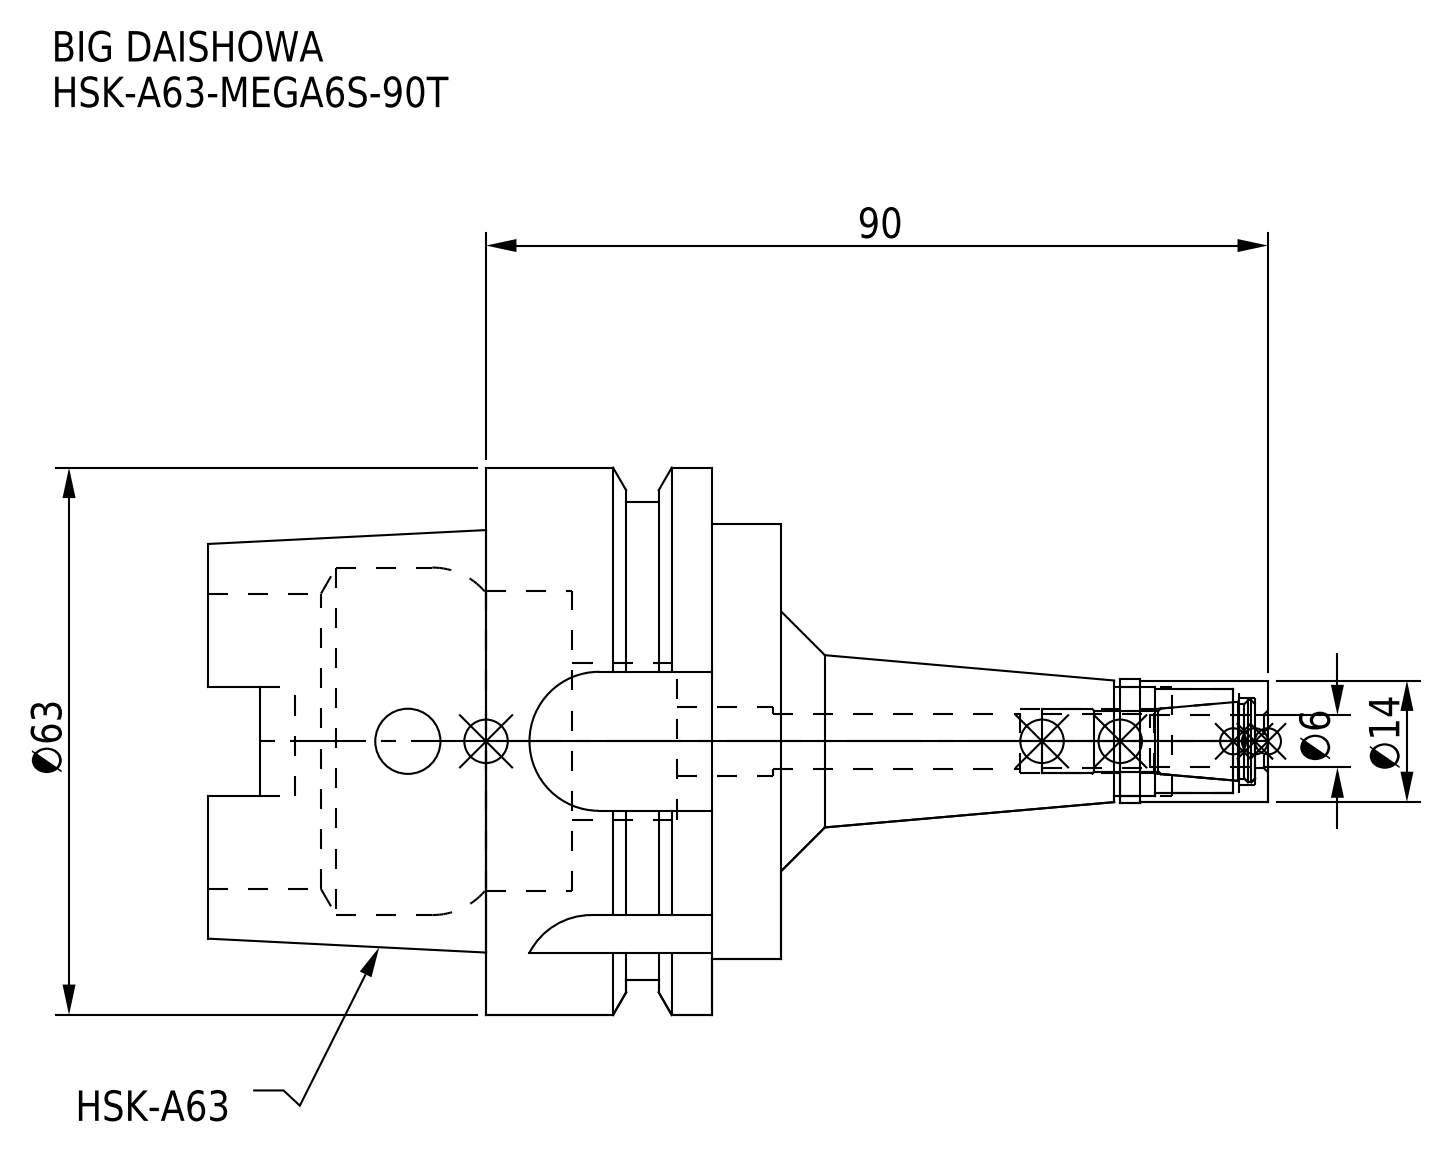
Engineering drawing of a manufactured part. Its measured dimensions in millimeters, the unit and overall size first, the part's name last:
Units: millimetres
Overall size (bounding box): 122 × 63 × 63
Round holes (diameter × count): ⌀6.1 ×1, ⌀6.4 ×1, ⌀7.4 ×1, ⌀7.5 ×1, ⌀8 ×1, ⌀10 ×1, ⌀12 ×1, ⌀12.5 ×1, ⌀18 ×1, ⌀34 ×1, ⌀34.5 ×1, ⌀40 ×1
Round bosses / shafts (diameter × count): ⌀63 ×1, ⌀55 ×1, ⌀50 ×1, ⌀14.3 ×1, ⌀14 ×1
Partial cylindrical surfaces — rounded edges, fillets, slot ends (radius × count): R2.88 ×4, R8 ×4
Main face-to-face distances: 34, 26, 8, 24.05, 16.05, 9.95, 66, 58, 41.95, 32
Volume: 107 374 mm³ · Surface area: 28 861 mm²
Bodies: 2 solids, 122 faces (47 planar, 53 cylindrical, 22 other)
Part name (STEP PRODUCT): HSK-A63-MEGA6S-90T-060.stp; HSK-A63-MEGA6S-90T; MGN6S_1.stp; HSK-A63-MEGA6S-90T-060-FreeParts (+3 more)
STEP written by: SolidWorks 2019 (CONFIG_CONTROL_DESIGN)
